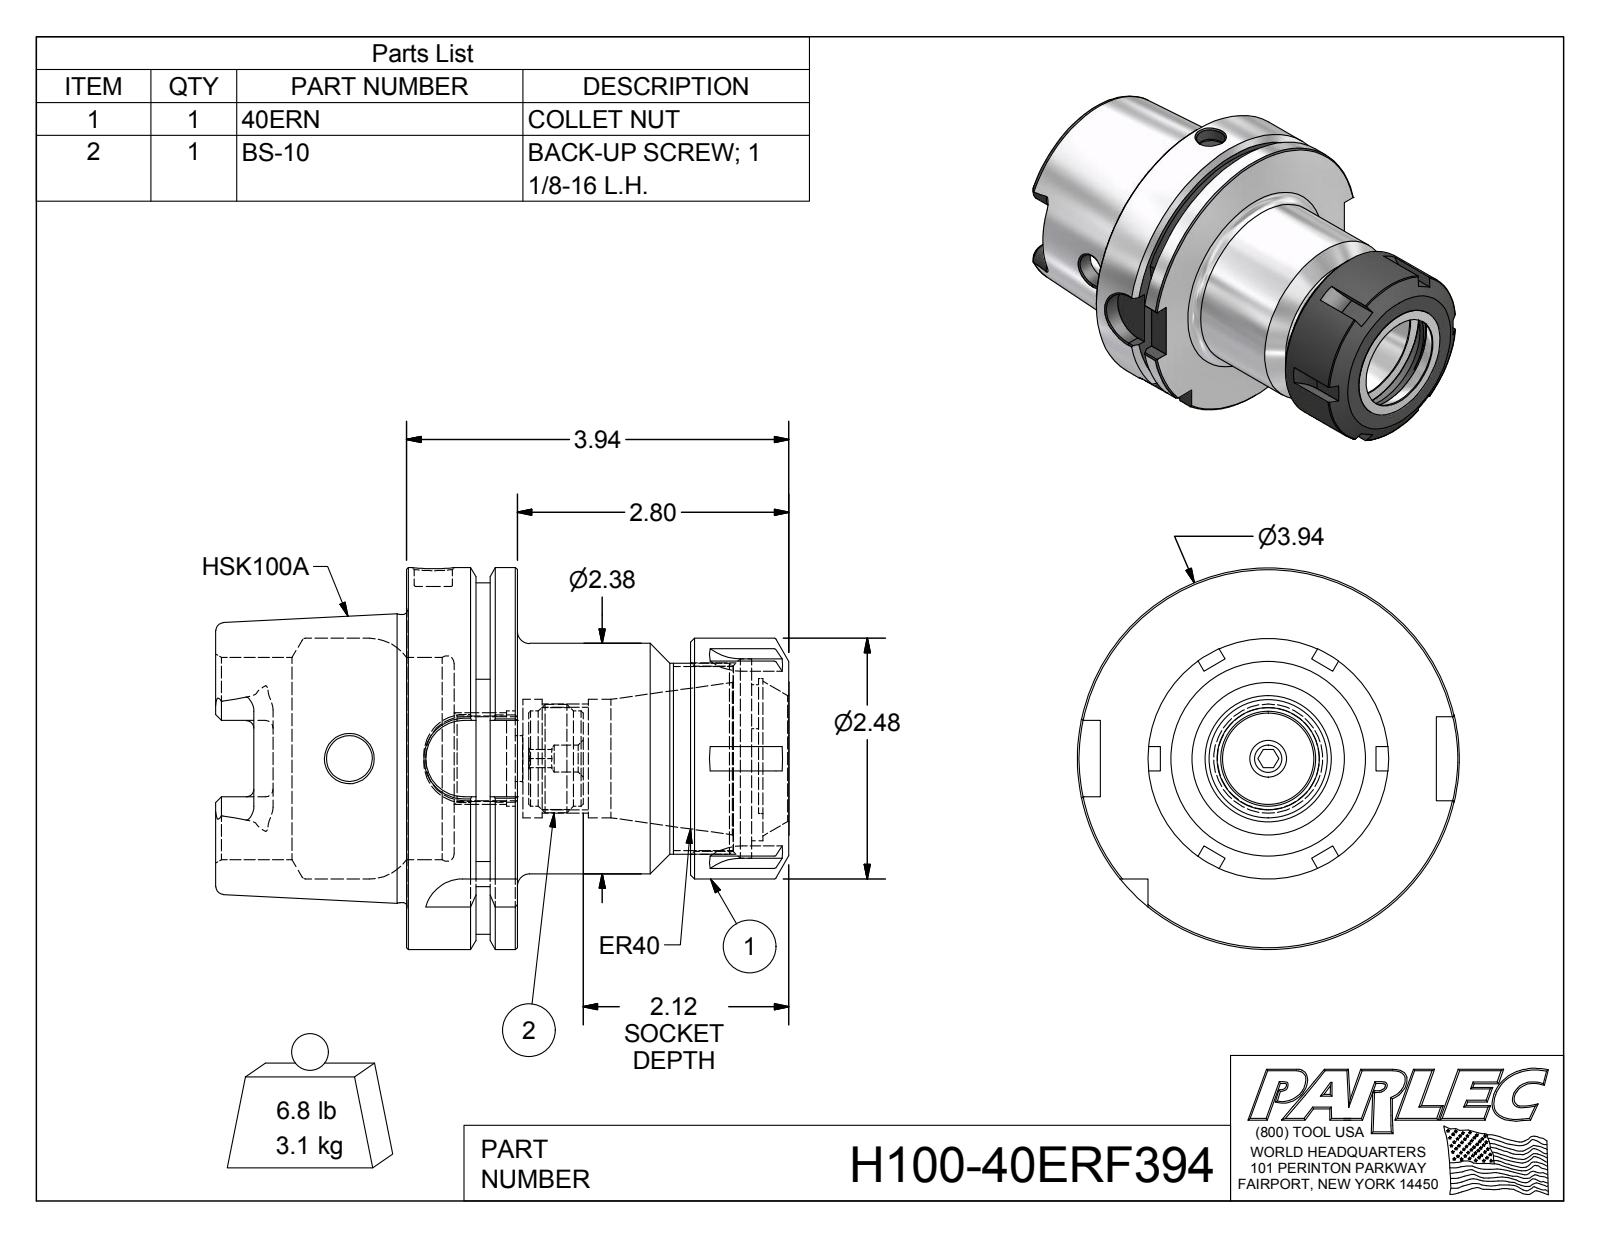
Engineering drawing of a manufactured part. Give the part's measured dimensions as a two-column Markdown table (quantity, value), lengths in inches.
| quantity | value |
| --- | --- |
| part name | H100-40ERF394; H100-40ER4-1; 40ERN; BS-10 |
| STEP written by | Autodesk Inventor 2012 (AUTOMOTIVE_DESIGN) |
| units | inches |
| bodies | 3 solids, 200 faces (77 planar, 55 cylindrical, 68 other) |
| overall size | 5.914 × 3.937 × 3.937 |
| volume | 24 in³ |
| surface area | 124.9 in² |
| round holes (diameter × count) | 0.472 × 2, 0.22 × 1, 0.28 × 1, 0.394 × 1, 0.881 × 1, 0.985 × 1, 1.057 × 1, 1.22 × 1, 1.225 × 1, 1.298 × 1, 1.909 × 1, 2.057 × 1 |
| round bosses / shafts (diameter × count) | 3.937 × 1, 2.967 × 1, 2.375 × 1, 1.969 × 1, 1.575 × 1, 1.118 × 1, 0.98 × 1 |
| partial cylindrical surfaces (radius × count) | 0.079 × 6, 0.501 × 6, 0.192 × 4, 0.394 × 4, 0.762 × 1, 0.787 × 1, 0.827 × 1, 1.811 × 1 |
| main face-to-face distances | 1.142, 0.492, 0.65, 2.436, 0.63, 2.928, 1.787, 1.969, 2.461, 3.11 |
